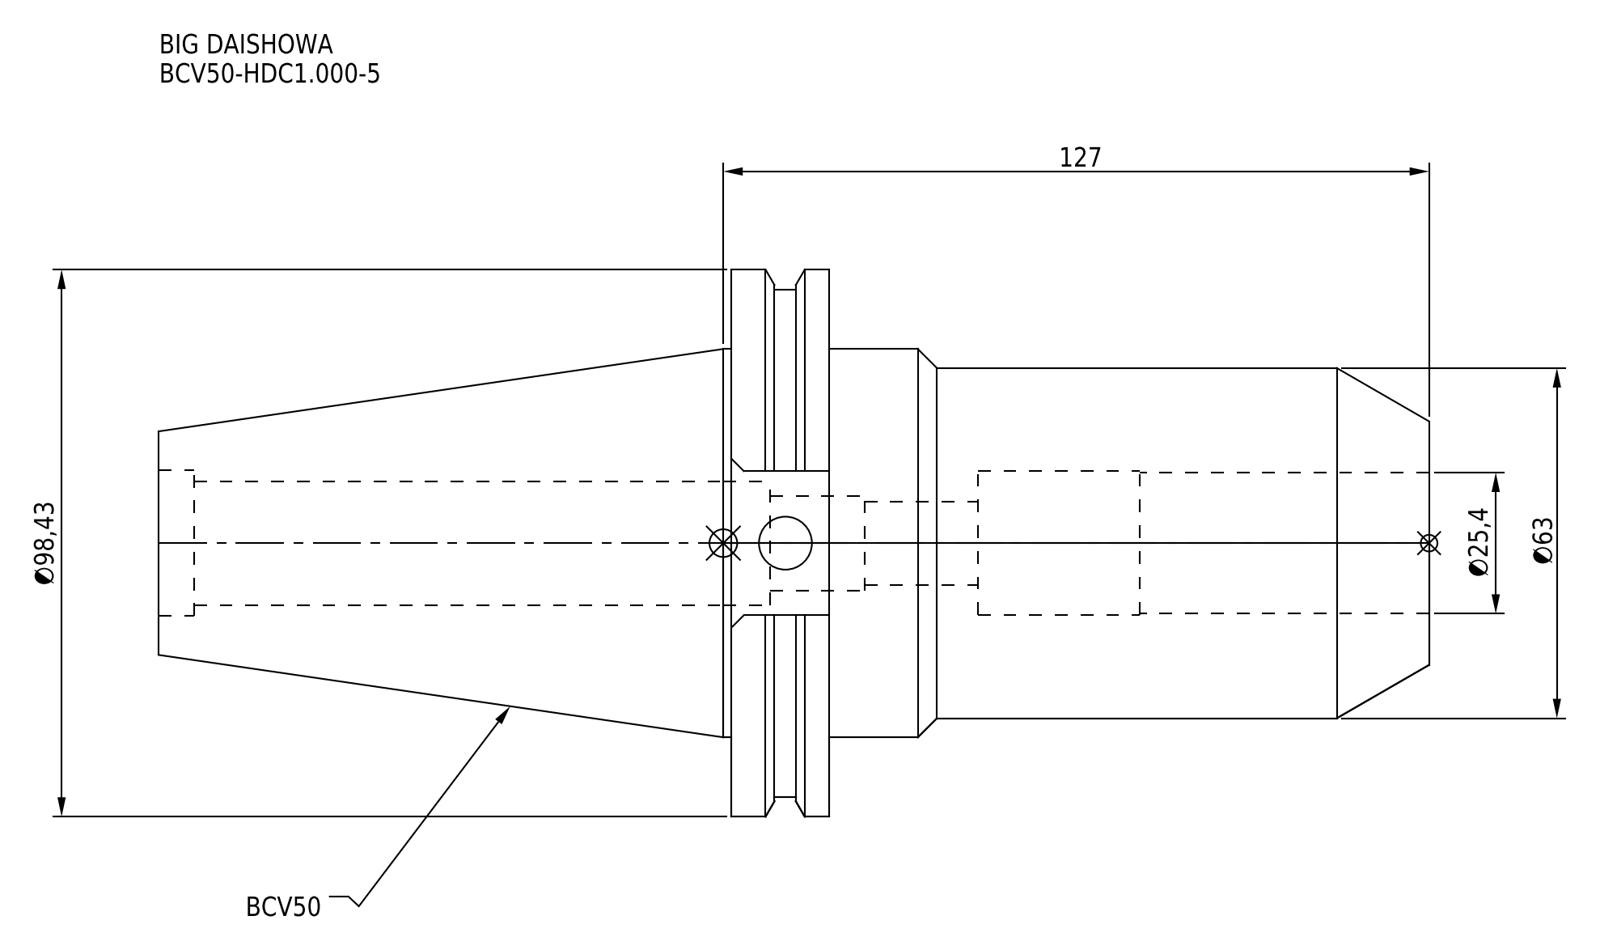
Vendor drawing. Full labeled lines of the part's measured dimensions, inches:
Part name (STEP PRODUCT): BCV50-HDC1_000-5
STEP written by: CREO PARAMETRIC BY PTC INC, 2016380 (AUTOMOTIVE_DESIGN)
Units: inches
Bodies: 1 solid, 62 faces (24 planar, 28 cylindrical, 10 other)
Overall size (bounding box): 9 × 3.875 × 3.738
Volume: 37.4 in³ · Surface area: 111.8 in²
Round holes (diameter × count): ⌀0.375 ×1, ⌀0.591 ×1, ⌀0.669 ×1, ⌀0.878 ×1, ⌀1 ×1, ⌀1.02 ×1, ⌀1.033 ×1
Round bosses / shafts (diameter × count): ⌀3.875 ×1, ⌀3.594 ×1, ⌀2.75 ×1, ⌀2.48 ×1
Main face-to-face distances: 0.691, 4.25, 4.941, 4.75, 9, 4.059, 2.872, 3.197, 1.053, 1.744
